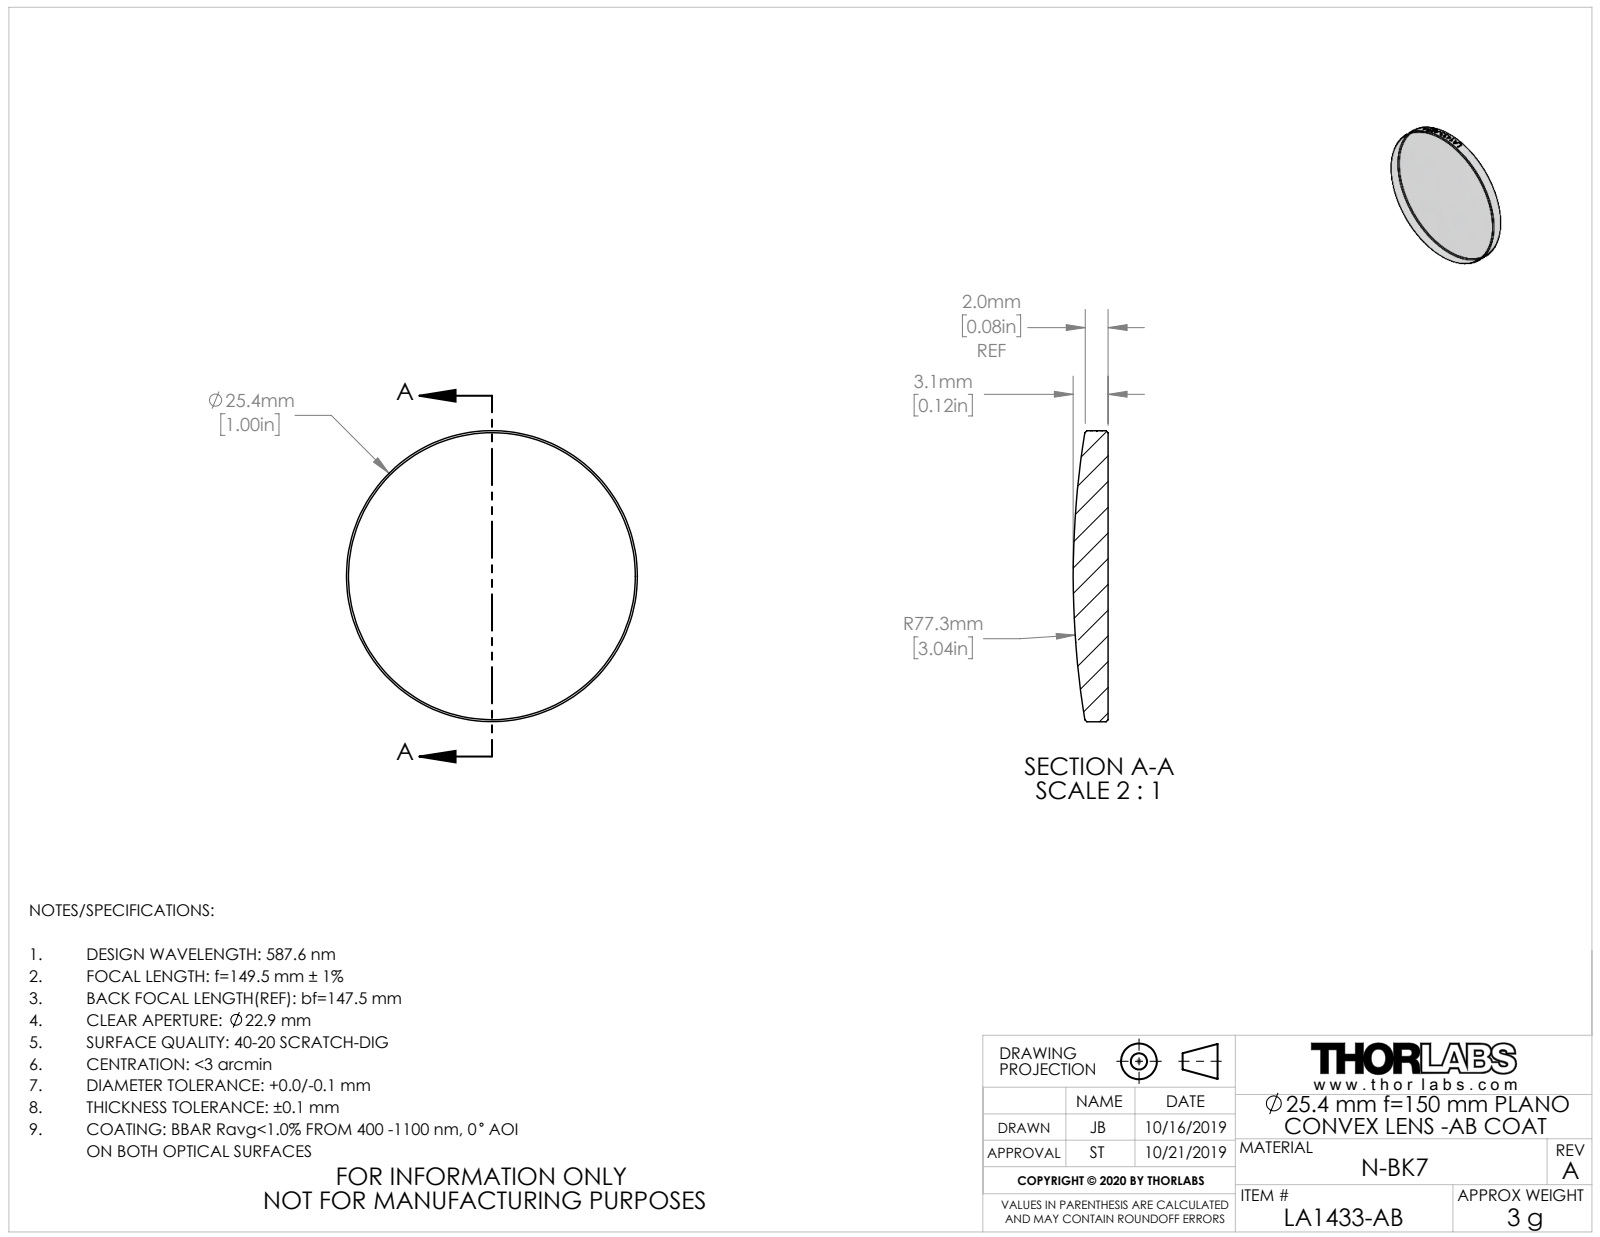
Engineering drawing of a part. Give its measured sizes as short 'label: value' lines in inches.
name: TTN195772-E0W
written by: SolidWorks 2018 (CONFIG_CONTROL_DESIGN)
unit: in
bodies: 1 solid, 27 faces (1 planar, 20 cylindrical, 6 other)
size: 1 × 1 × 0.12
volume: 0.078 in³; area: 1.801 in²
bosses: 1× ⌀1
